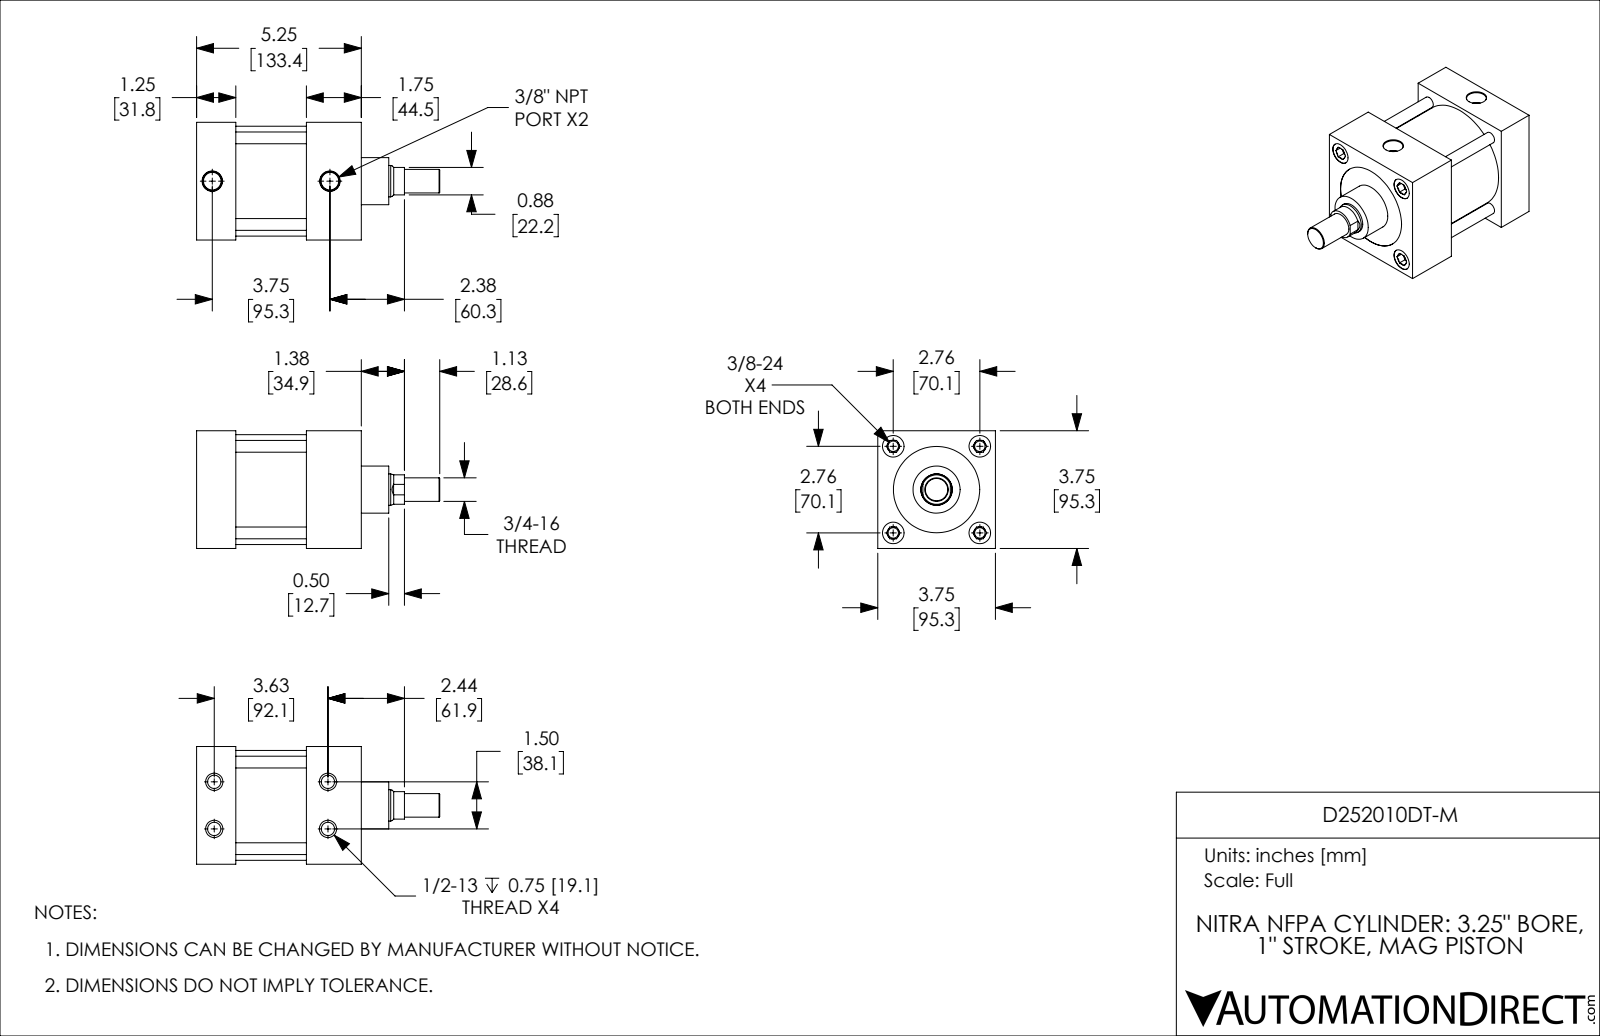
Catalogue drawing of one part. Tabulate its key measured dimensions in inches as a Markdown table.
| quantity | value |
| --- | --- |
| part name | D252010DT-M; D252010DT-M_BODY; D252010DT-M_PISTON_KK1 |
| STEP written by | SolidWorks 2019 (CONFIG_CONTROL_DESIGN) |
| units | inches |
| bodies | 2 solids, 198 faces (58 planar, 62 cylindrical, 78 other) |
| overall size | 7.75 × 3.75 × 3.75 |
| volume | 57.49 in³ |
| surface area | 230.4 in² |
| round holes (diameter × count) | 0.332 × 4, 0.422 × 4, 0.687 × 4, 0.562 × 2, 1 × 1, 2.75 × 1, 3.251 × 1 |
| round bosses / shafts (diameter × count) | 0.375 × 4, 3.501 × 1, 3.249 × 1, 1.5 × 1, 0.999 × 1, 0.75 × 1 |
| partial cylindrical surfaces (radius × count) | 0.469 × 1 |
| main face-to-face distances | 1.25, 3.75, 3.5, 2.25, 2.5, 1, 5.25, 4, 2.75, 1.75 |
| hole center spacings | 0.753, 1.952, 2.76, 3.763, 1.5, 3.625, 3.903, 3.923 |
